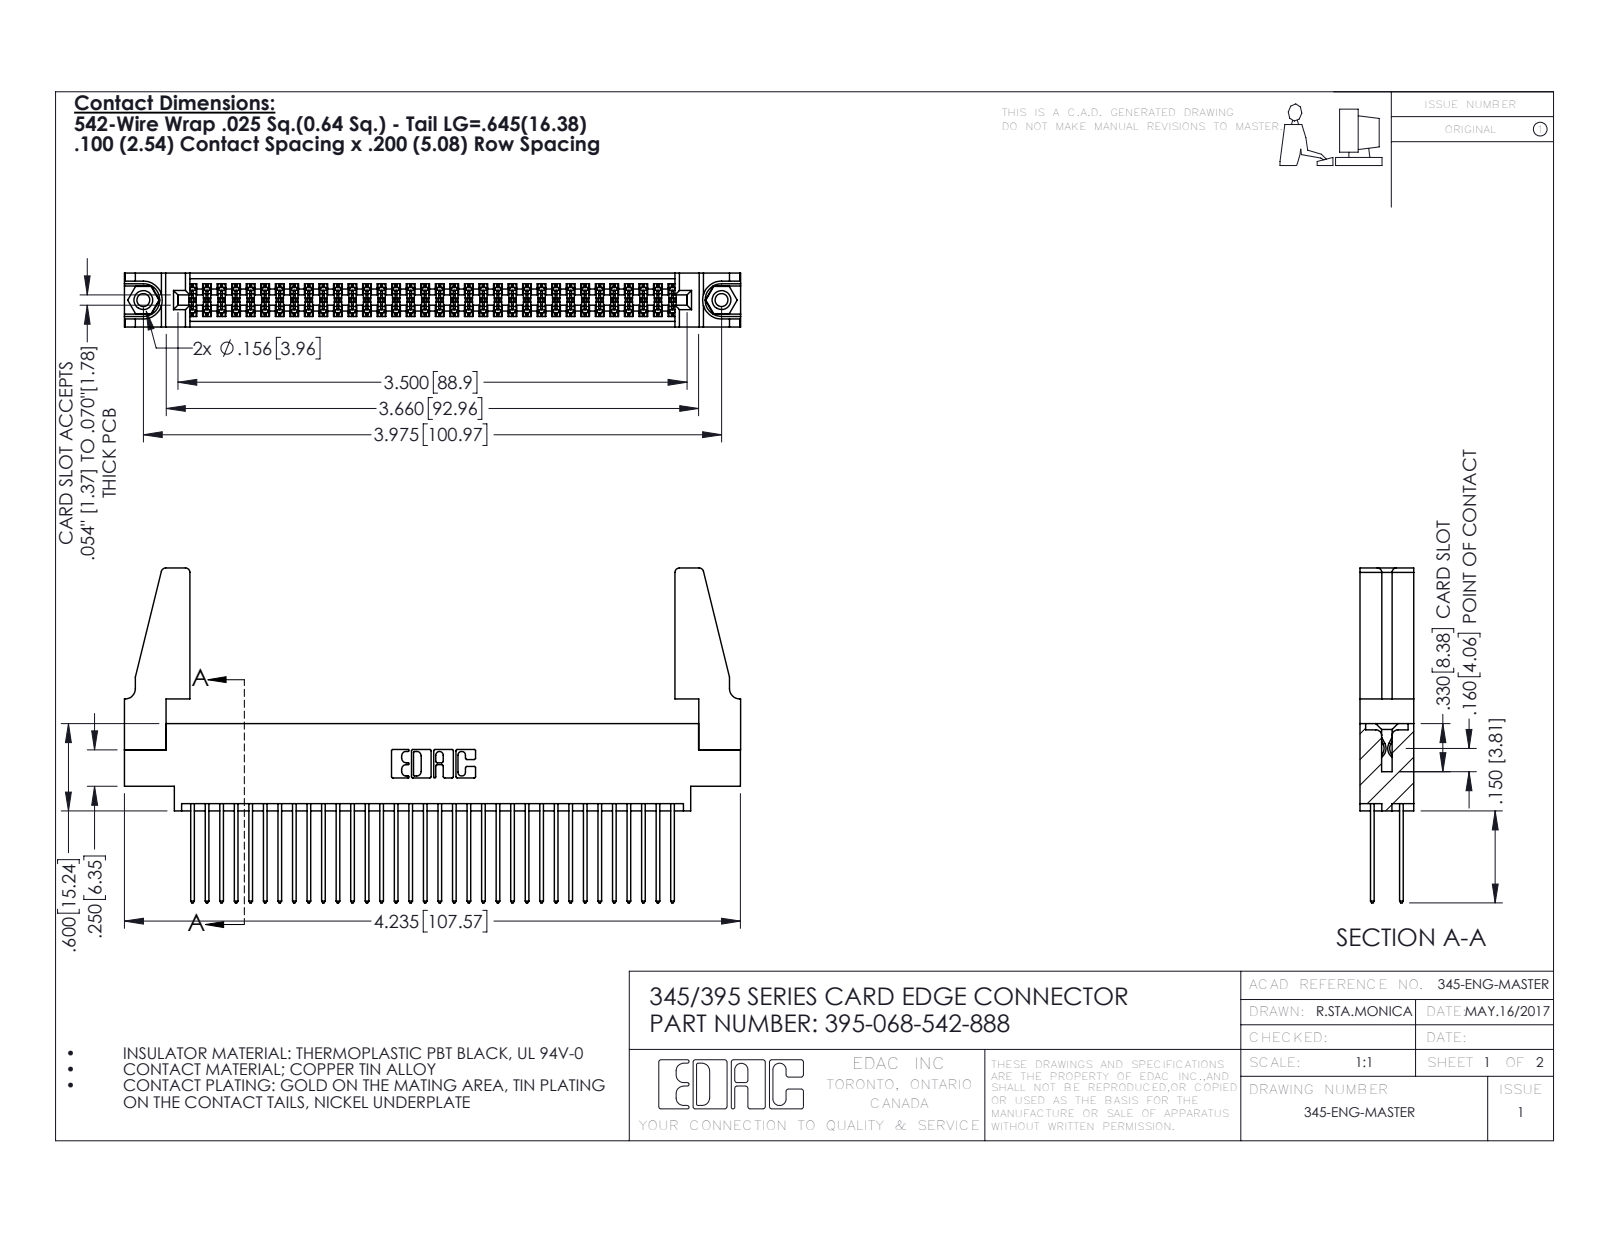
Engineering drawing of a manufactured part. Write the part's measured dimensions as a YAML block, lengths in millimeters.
part_name: "345-250-001_345-250-001-102; 345 Part_0.170 Offset - 0.156 Dia-TH; 345-220-078_345-220-088; 345-292-001_345-293-142 (+1 more)"
step_written_by: "SolidWorks 2016 (CONFIG_CONTROL_DESIGN)"
units: millimeters
bodies: {solids: 73, faces: 3654, planar: 2400, cylindrical: 1238, other: 16}
overall_size: [107.6, 58.5, 9.4]
volume: 13800
surface_area: 20230
round_holes:
  - {diameter: 2.3, count: 2}
  - {diameter: 3.2, count: 2}
  - {diameter: 4, count: 2}
  - {diameter: 1.6, count: 1}
round_bosses_or_shafts:
  - {diameter: 3.9, count: 2}
partial_cylinders:
  - {radius: 0.2, count: 102}
  - {radius: 0.3, count: 68}
  - {radius: 0.3, count: 22}
  - {radius: 0.8, count: 8}
  - {radius: 0.2, count: 6}
  - {radius: 0.8, count: 6}
  - {radius: 0.7, count: 3}
  - {radius: 0.4, count: 2}
face_to_face_distances: [1.8, 7.6, 9.4, 5.1, 2.5, 6.9, 0.6, 5.7, 4.4, 3.8]
hole_center_spacings: [6.9, 95, 101]
